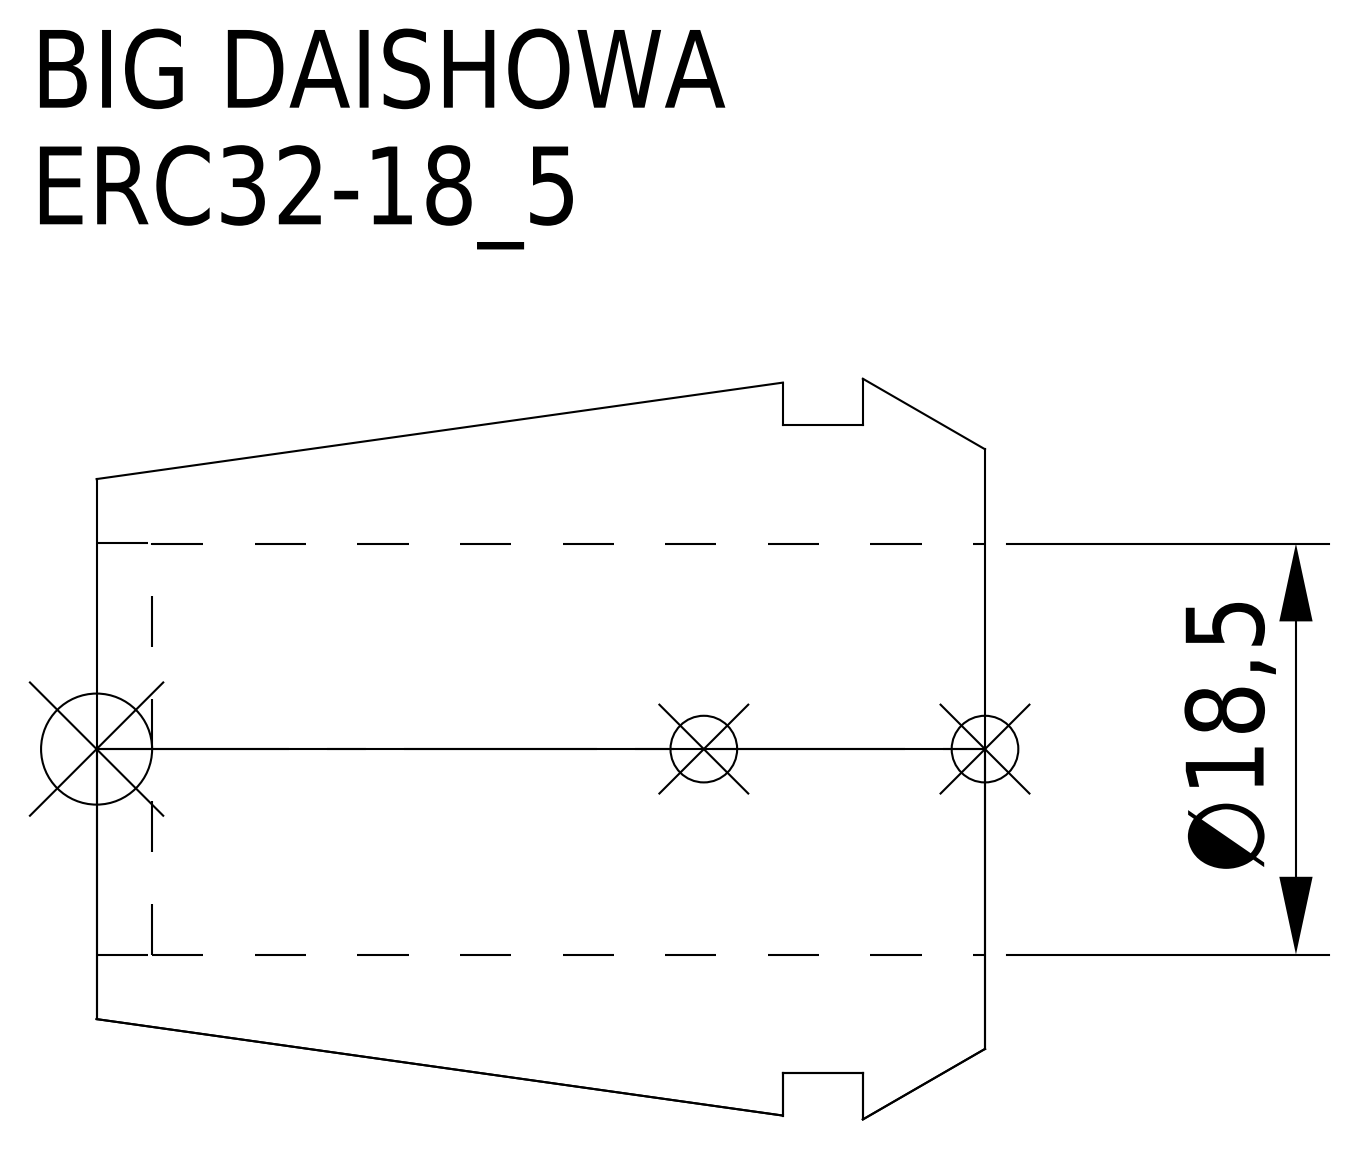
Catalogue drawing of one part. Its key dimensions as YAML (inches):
part_name: "ERC32-18_5"
step_written_by: "CREO PARAMETRIC BY PTC INC, 2016380 (AUTOMOTIVE_DESIGN)"
units: inches
bodies: {solids: 1, faces: 15, planar: 5, cylindrical: 6, other: 4}
overall_size: [1.575, 1.313, 1.313]
volume: 0.957
surface_area: 10.78
round_holes:
  - {diameter: 0.728, count: 1}
  - {diameter: 0.73, count: 1}
round_bosses_or_shafts:
  - {diameter: 1.15, count: 1}
face_to_face_distances: [0.217, 1.575, 1.358, 0.358, 0.142, 1.217, 1.476, 1.26, 1.118, 0.098]
